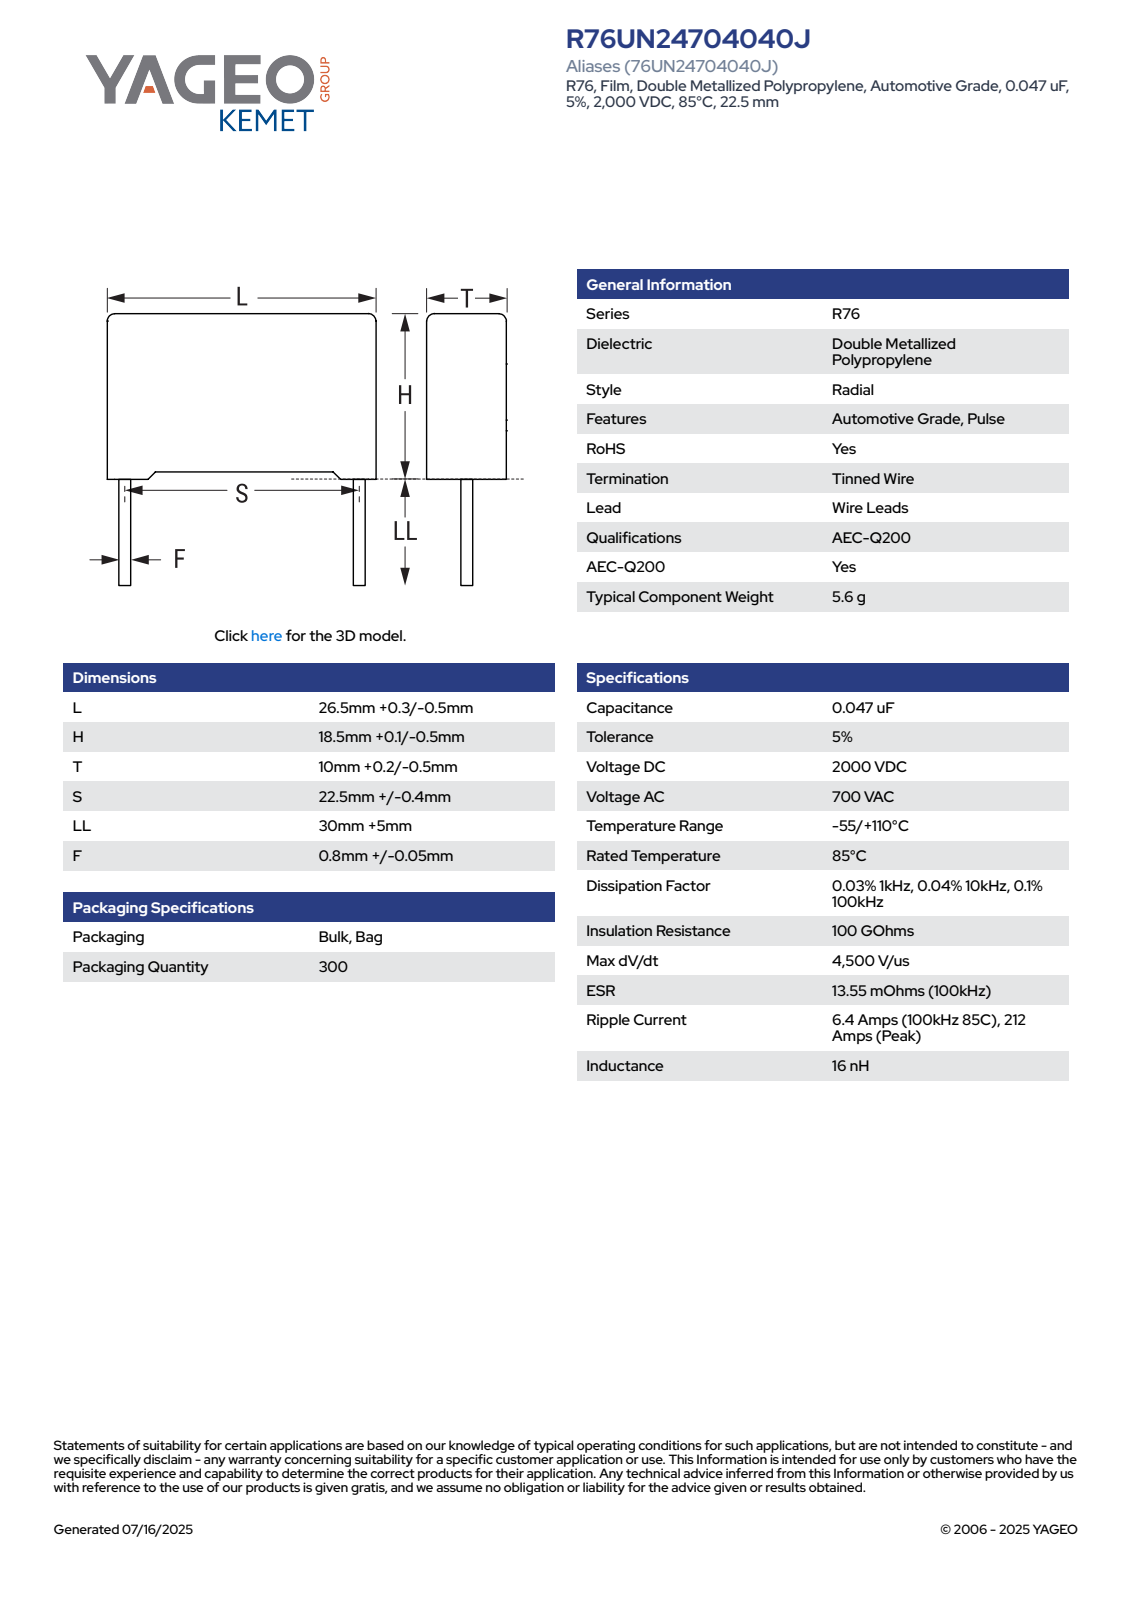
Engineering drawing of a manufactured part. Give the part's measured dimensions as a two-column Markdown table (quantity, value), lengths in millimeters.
| quantity | value |
| --- | --- |
| part name | CFR_RB2_26.5X18.5X10_L26.8H18.6T10.2S22.5LL35F0.85 |
| STEP written by | SolidWorks 2021 (AUTOMOTIVE_DESIGN) |
| units | millimeters |
| bodies | 4 solids, 85 faces (77 planar, 8 cylindrical, 0 other) |
| overall size | 53.6 × 26.8 × 10.21 |
| volume | 4 942 mm³ |
| surface area | 2 155 mm² |
| round bosses / shafts (diameter × count) | 0.85 × 2 |
| partial cylindrical surfaces (radius × count) | 0.5 × 4 |
| main face-to-face distances | 10.2, 17.85, 26.8, 17.96, 0.75, 0.64, 18.6, 0.89, 9.31, 25.91 |
